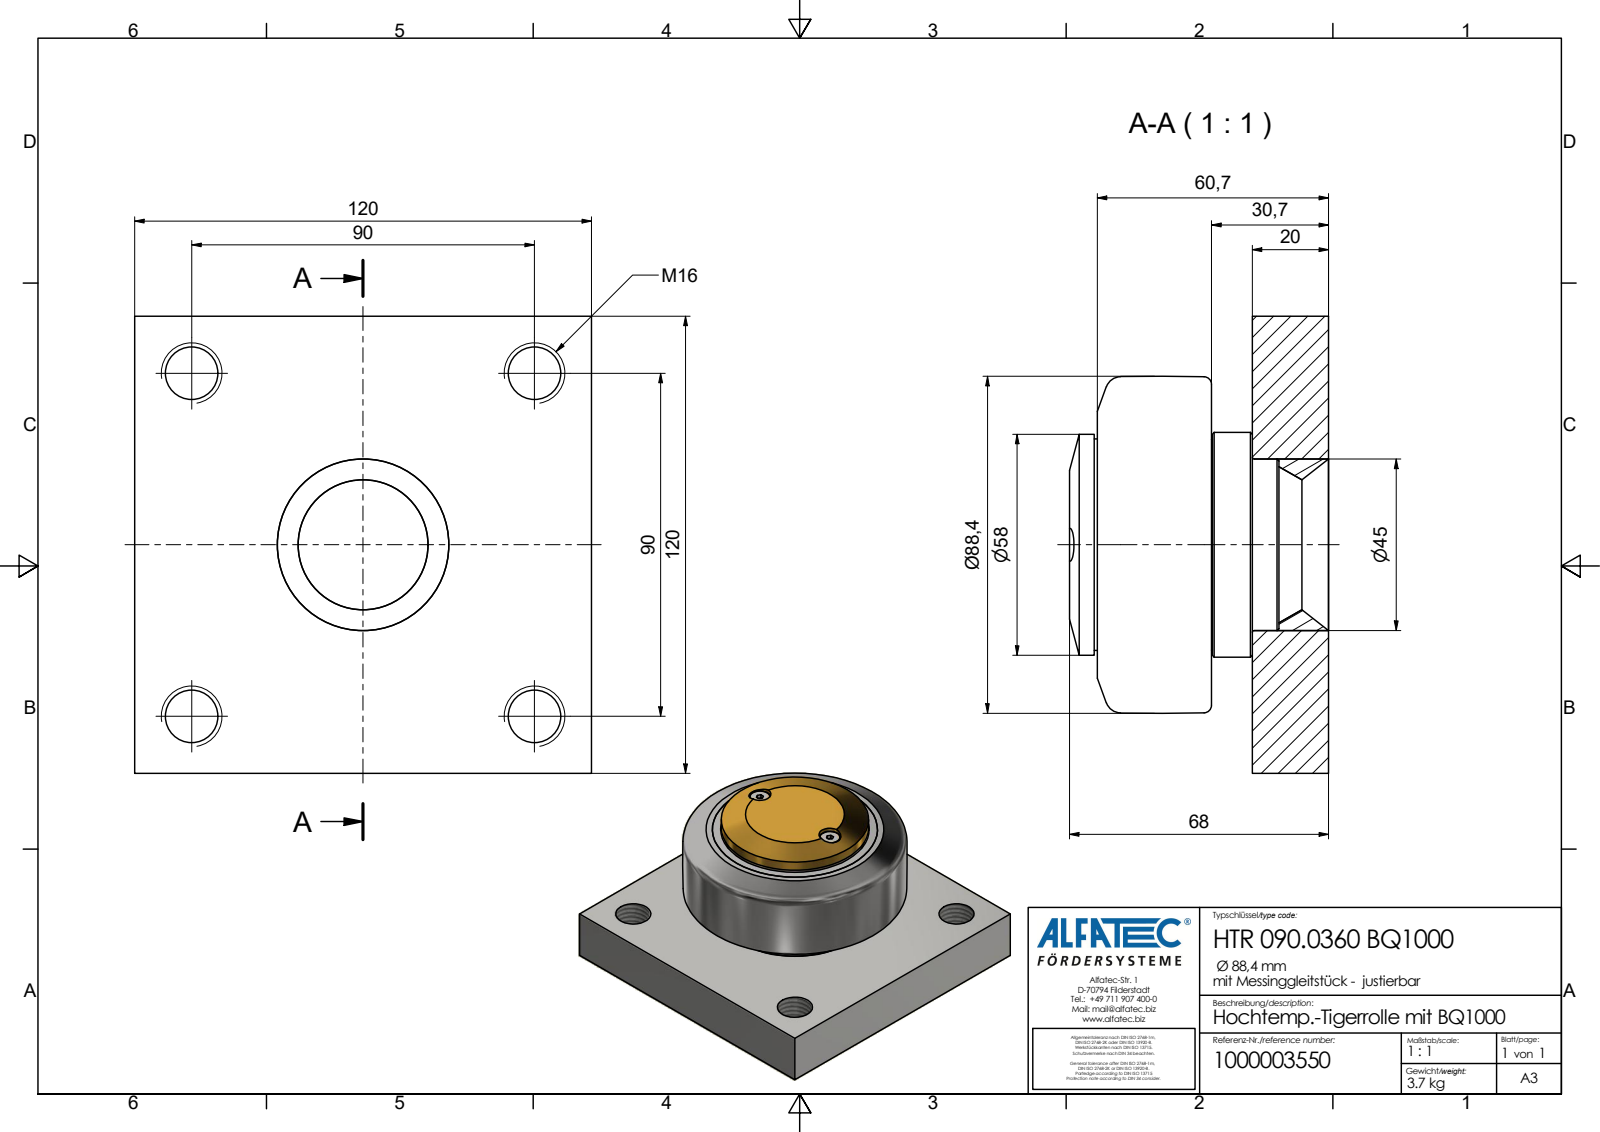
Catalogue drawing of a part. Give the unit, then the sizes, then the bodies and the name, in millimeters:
Units: millimetres
Overall size (bounding box): 120 × 120 × 68
Round holes (diameter × count): ⌀13.84 ×4, ⌀8.6 ×2
Round bosses / shafts (diameter × count): ⌀7.8 ×2, ⌀59 ×1, ⌀58 ×1, ⌀55.5 ×1, ⌀55.3 ×1
Main face-to-face distances: 20, 120, 30.7, 10.7, 60.7, 40.7, 30, 68, 48, 37.3
Hole centre spacings: 51.72, 78.65, 90, 127.28, 39
Volume: 492 692 mm³ · Surface area: 59 158 mm²
Bodies: 1 solid, 50 faces (28 planar, 12 cylindrical, 10 other)
Part name (STEP PRODUCT): HTR 090.0360 BQ1000_Kontur
STEP written by: Autodesk Inventor 2020 (AP242_MANAGED_MODEL_BASED_3D_ENGINEERING_MIM_LF)
